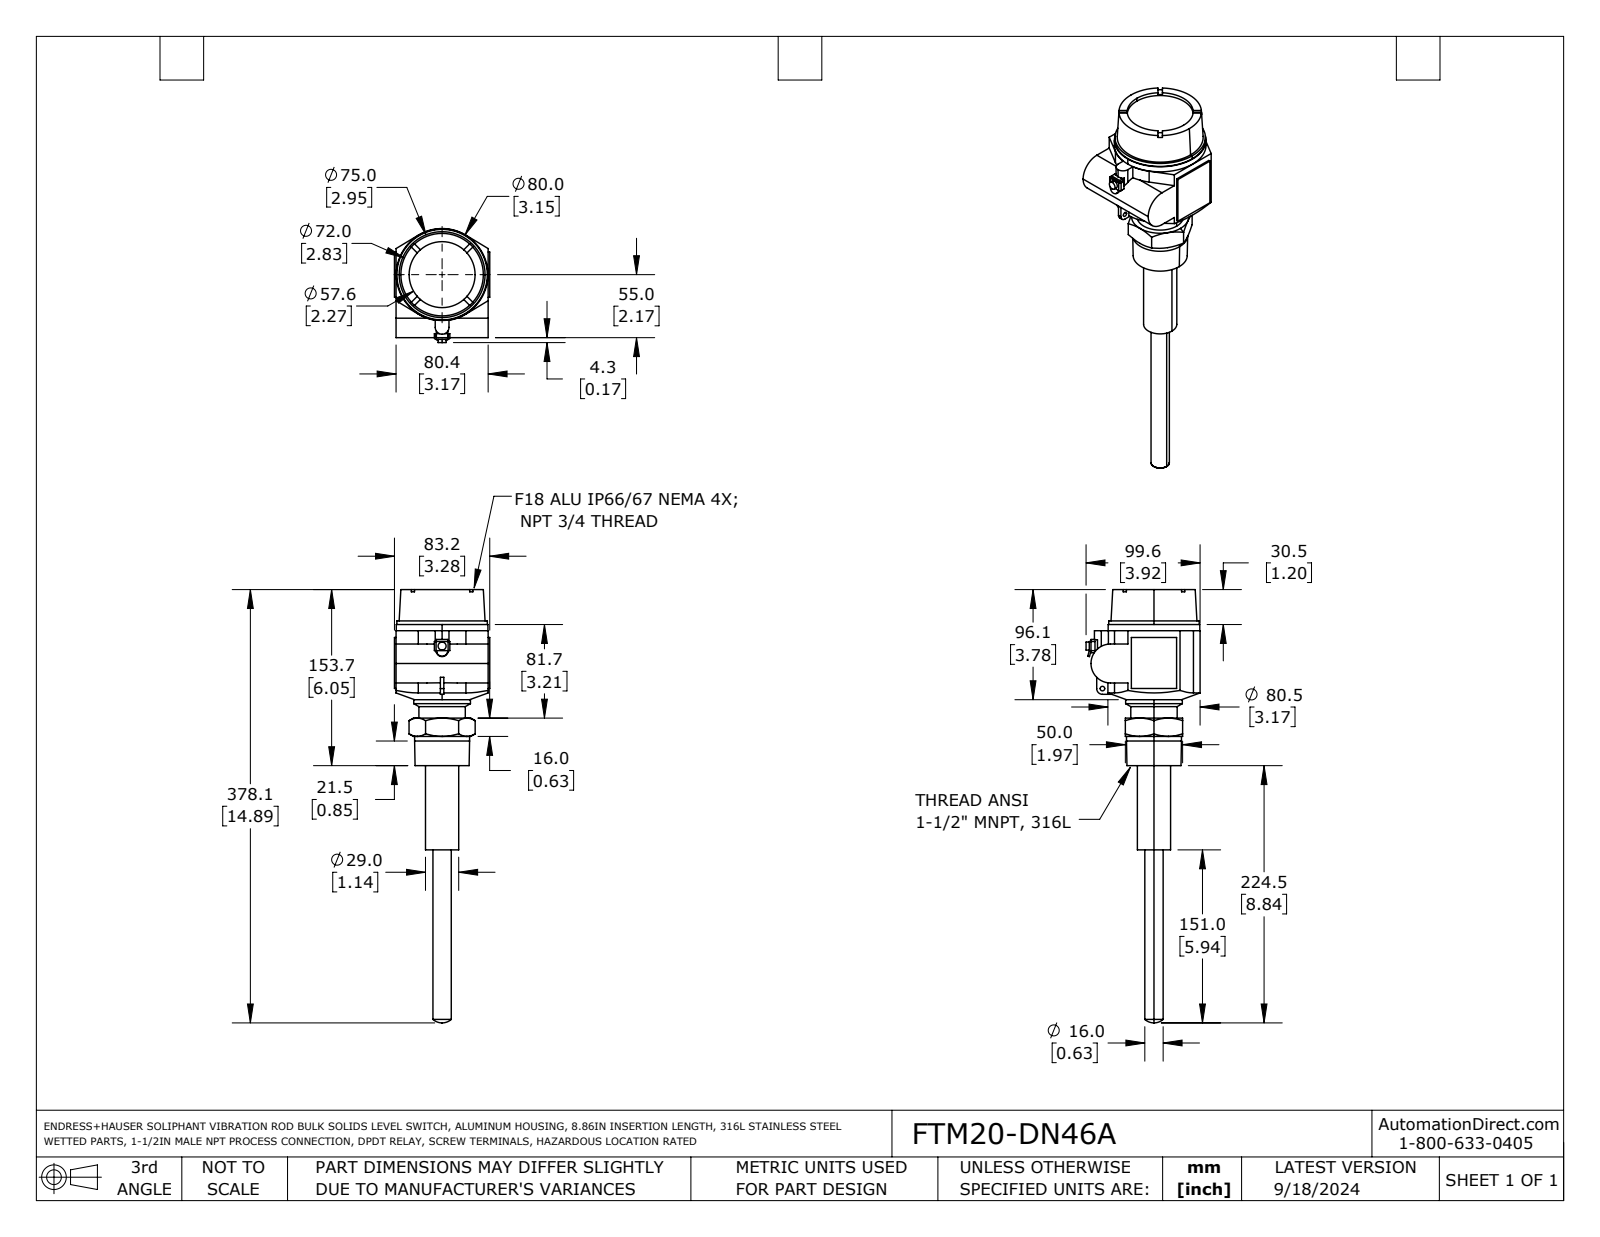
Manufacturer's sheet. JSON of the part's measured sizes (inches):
{"part_name": "FTM20-DN46A", "step_written_by": "SolidWorks 2021 (AUTOMOTIVE_DESIGN)", "units": "inches", "bodies": {"solids": 1, "faces": 151, "planar": 88, "cylindrical": 36, "other": 27}, "overall_size": [14.888, 3.919, 3.276], "volume_in3": 42.85, "surface_area_in2": 99.39, "round_holes": [[0.157, 1], [2.268, 1]], "round_bosses_or_shafts": [[3.15, 1], [3.11, 1], [1.949, 1], [1.89, 1], [1.594, 1], [1.142, 1], [0.63, 1], [0.276, 1]], "partial_cylinders_radius": [[0.059, 3], [0.197, 2], [0.236, 1], [0.669, 1], [1.585, 1]], "face_to_face_distances": [0.055, 3.22, 3.276, 3.165, 0.118, 1.969, 5.931, 6.049, 3.169, 1.634]}
